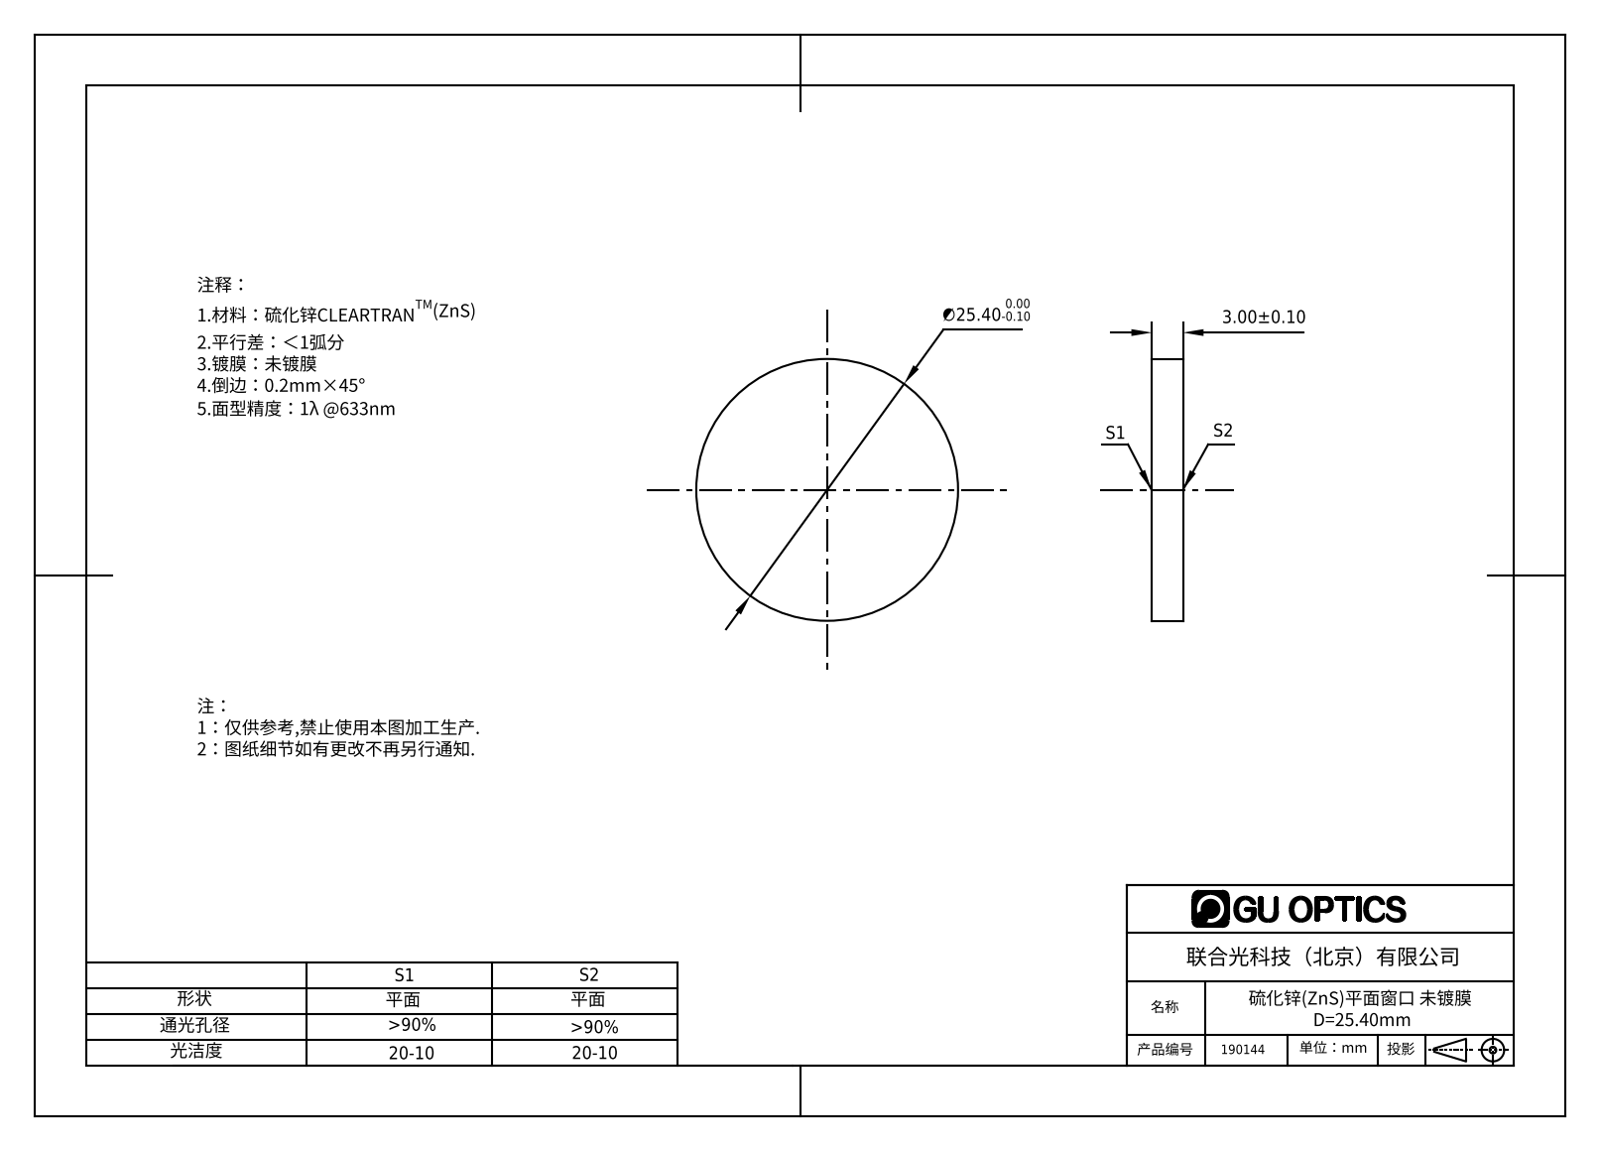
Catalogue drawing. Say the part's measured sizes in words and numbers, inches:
The part is named "190144". Its 3-D file was written by "SolidWorks 2016 (AUTOMOTIVE_DESIGN)". It is 1 solid with 4 faces: 2 planar, 2 cylindrical and 0 other. Overall it measures 1 by 1 by 0.118 inches. Its volume is 0.093 cubic inches and its surface area 1.942 square inches. Round bosses or shafts: 1 of diameter 1. The main face-to-face distances are 0.118.
